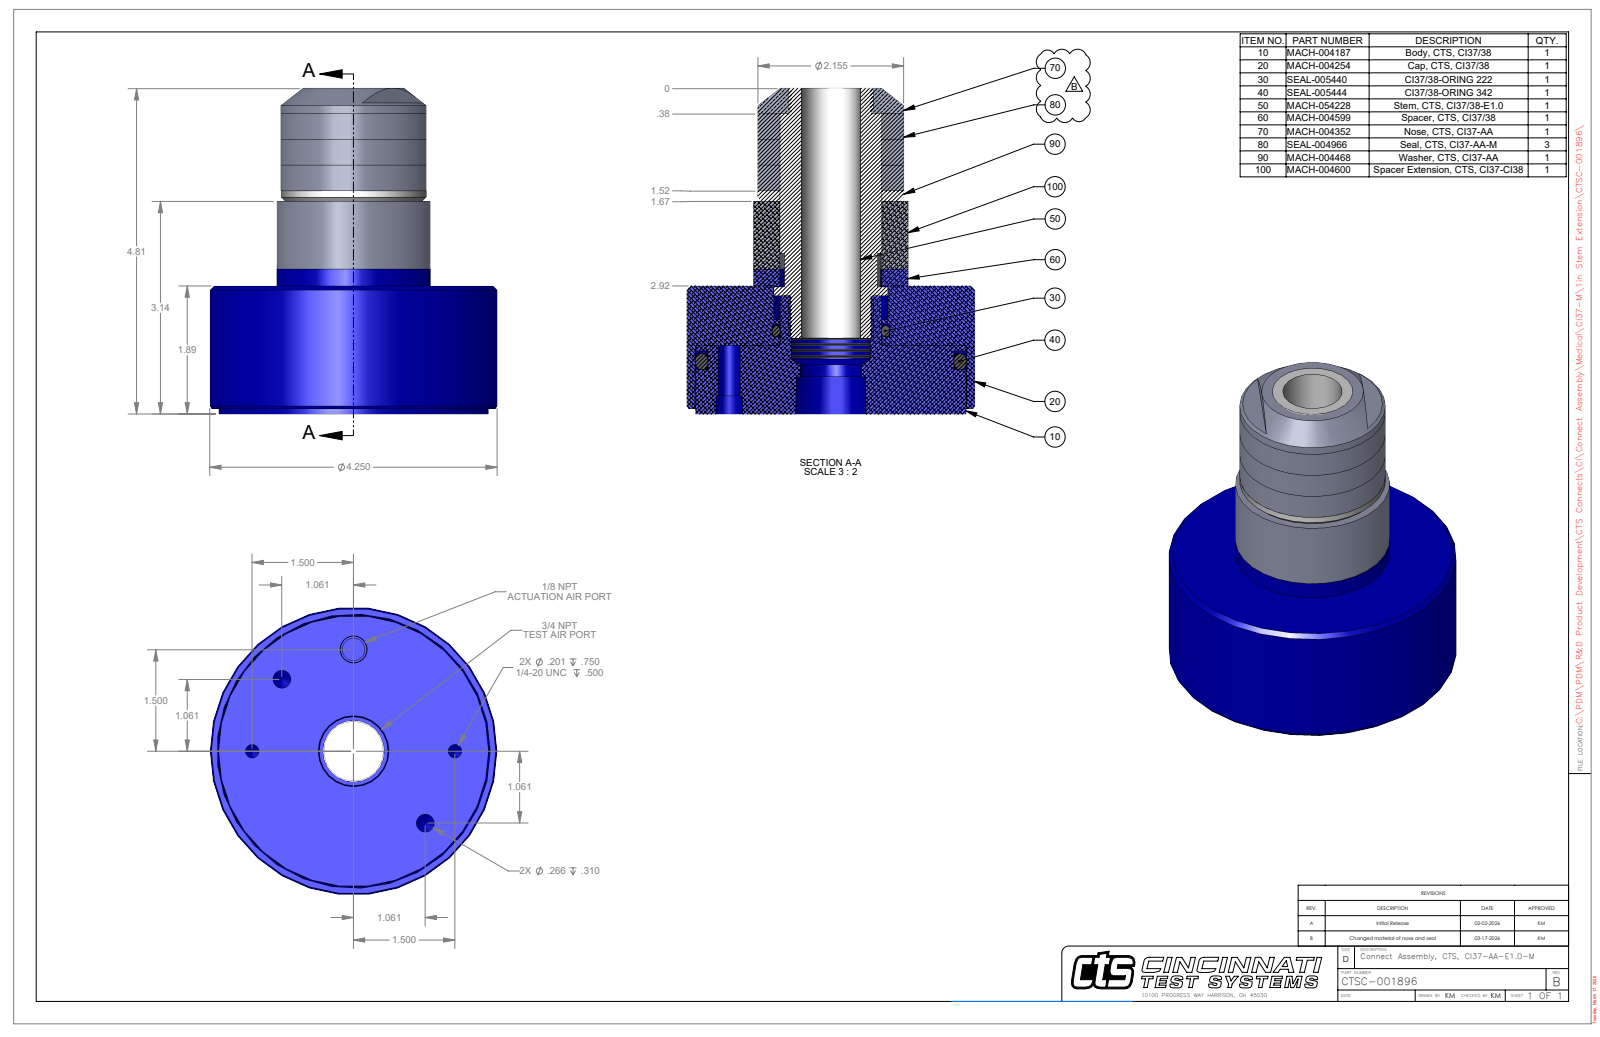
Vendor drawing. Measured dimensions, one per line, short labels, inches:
name: CTSC-001896
written by: SolidWorks 2023 (AUTOMOTIVE_DESIGN)
unit: in
bodies: 8 solids, 80 faces (38 planar, 29 cylindrical, 13 other)
size: 4.813 × 4.25 × 4.25
volume: 34.2 in³; area: 148.3 in²
holes: 2× ⌀0.201, 2× ⌀0.266, 1× ⌀0.332, 1× ⌀0.88, 1× ⌀0.906, 1× ⌀1.172, 1× ⌀1.495, 1× ⌀1.51, 1× ⌀1.688, 1× ⌀4
bosses: 1× ⌀4.25, 1× ⌀3.992, 1× ⌀2.281, 1× ⌀2.155, 1× ⌀1.674, 1× ⌀1.498, 1× ⌀1.25
face distances: 1.893, 0.38, 0.76, 2.143, 0.25, 4.435, 2.542, 2.292, 1.25, 3.675
hole spacings: 1.5, 1.148, 2.772, 2.121, 3
